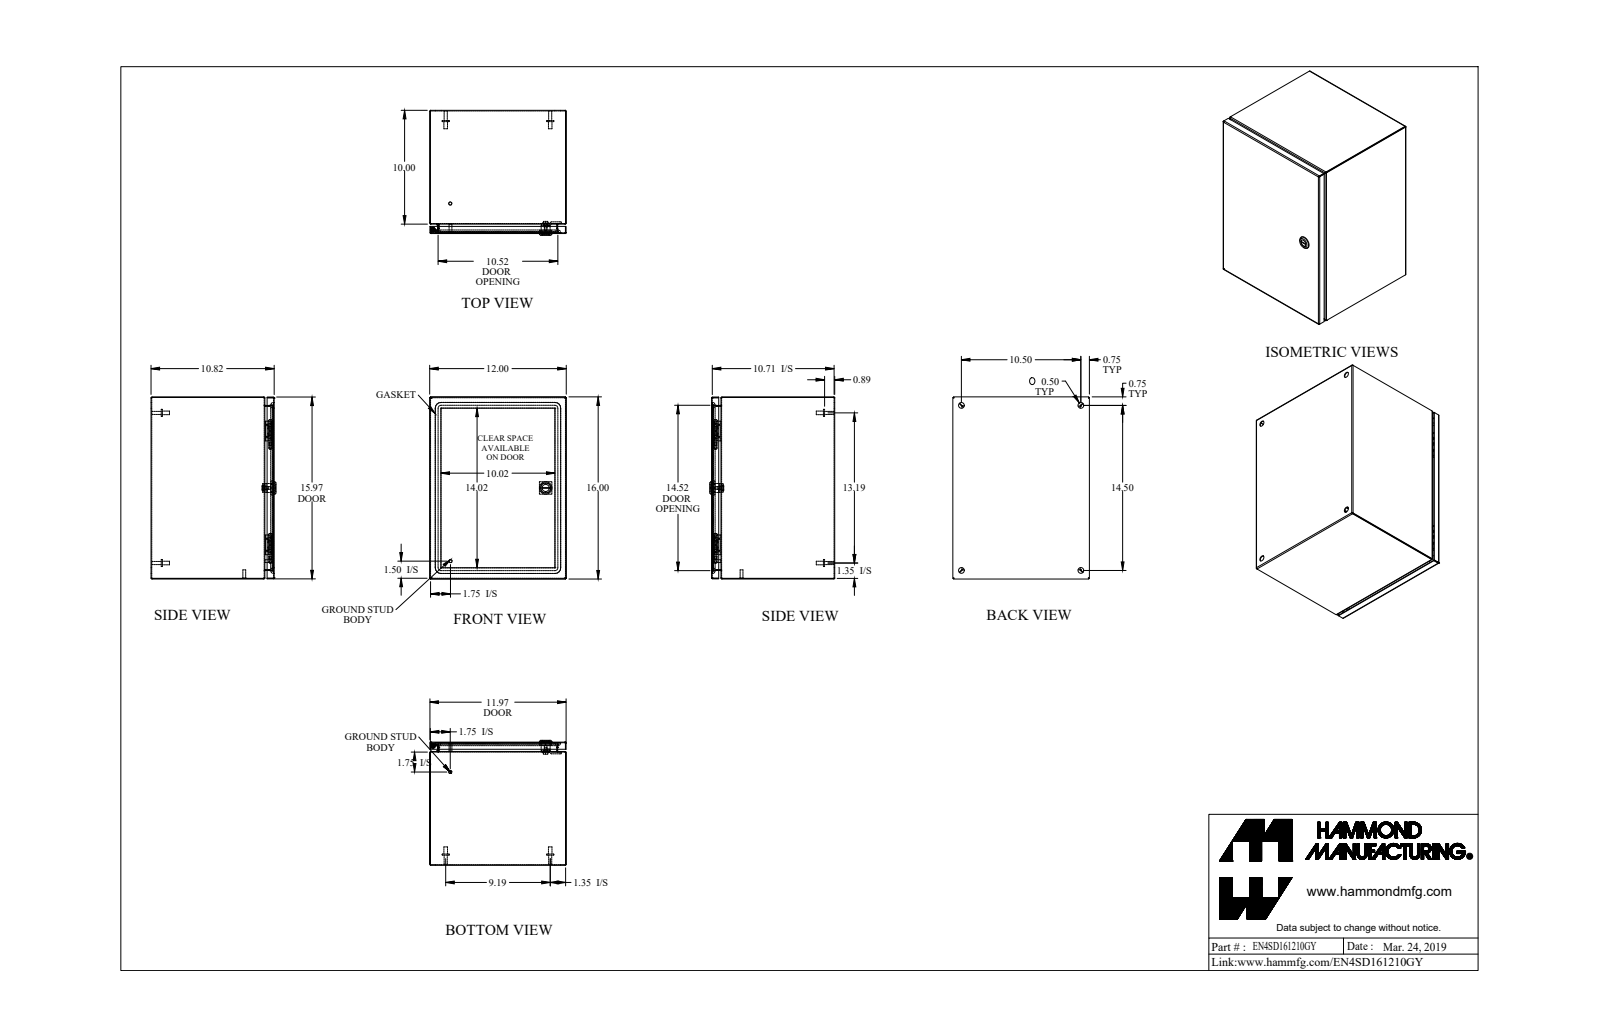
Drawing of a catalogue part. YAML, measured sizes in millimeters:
part_name: "EN4SD161210GY_Default"
step_written_by: "SolidWorks 2019 (CONFIG_CONTROL_DESIGN)"
units: millimeters
bodies: {solids: 21, faces: 634, planar: 285, cylindrical: 213, other: 136}
overall_size: [406.4, 304.8, 278.9]
volume: 1076000
surface_area: 1439000
round_holes:
  - {diameter: 12.7, count: 4}
  - {diameter: 4.4, count: 1}
  - {diameter: 5.9, count: 1}
  - {diameter: 6.1, count: 1}
  - {diameter: 6.1, count: 1}
  - {diameter: 15.9, count: 1}
  - {diameter: 19.9, count: 1}
round_bosses_or_shafts:
  - {diameter: 15.9, count: 4}
  - {diameter: 8, count: 4}
  - {diameter: 6.9, count: 4}
  - {diameter: 7.1, count: 2}
  - {diameter: 6.4, count: 2}
  - {diameter: 27.9, count: 1}
  - {diameter: 13.3, count: 1}
  - {diameter: 11.6, count: 1}
partial_cylinders:
  - {radius: 0.7, count: 21}
  - {radius: 2.2, count: 21}
  - {radius: 6.4, count: 16}
  - {radius: 482.6, count: 8}
  - {radius: 0.2, count: 4}
  - {radius: 1.6, count: 4}
  - {radius: 12.7, count: 4}
  - {radius: 3.2, count: 2}
face_to_face_distances: [1.4, 273.4, 303.4, 405, 272, 274.9, 301.9, 304.8, 403.5, 406.4]
hole_center_spacings: [266.7, 368.3, 454.7, 186.1, 186.1, 302.3, 302.4]
